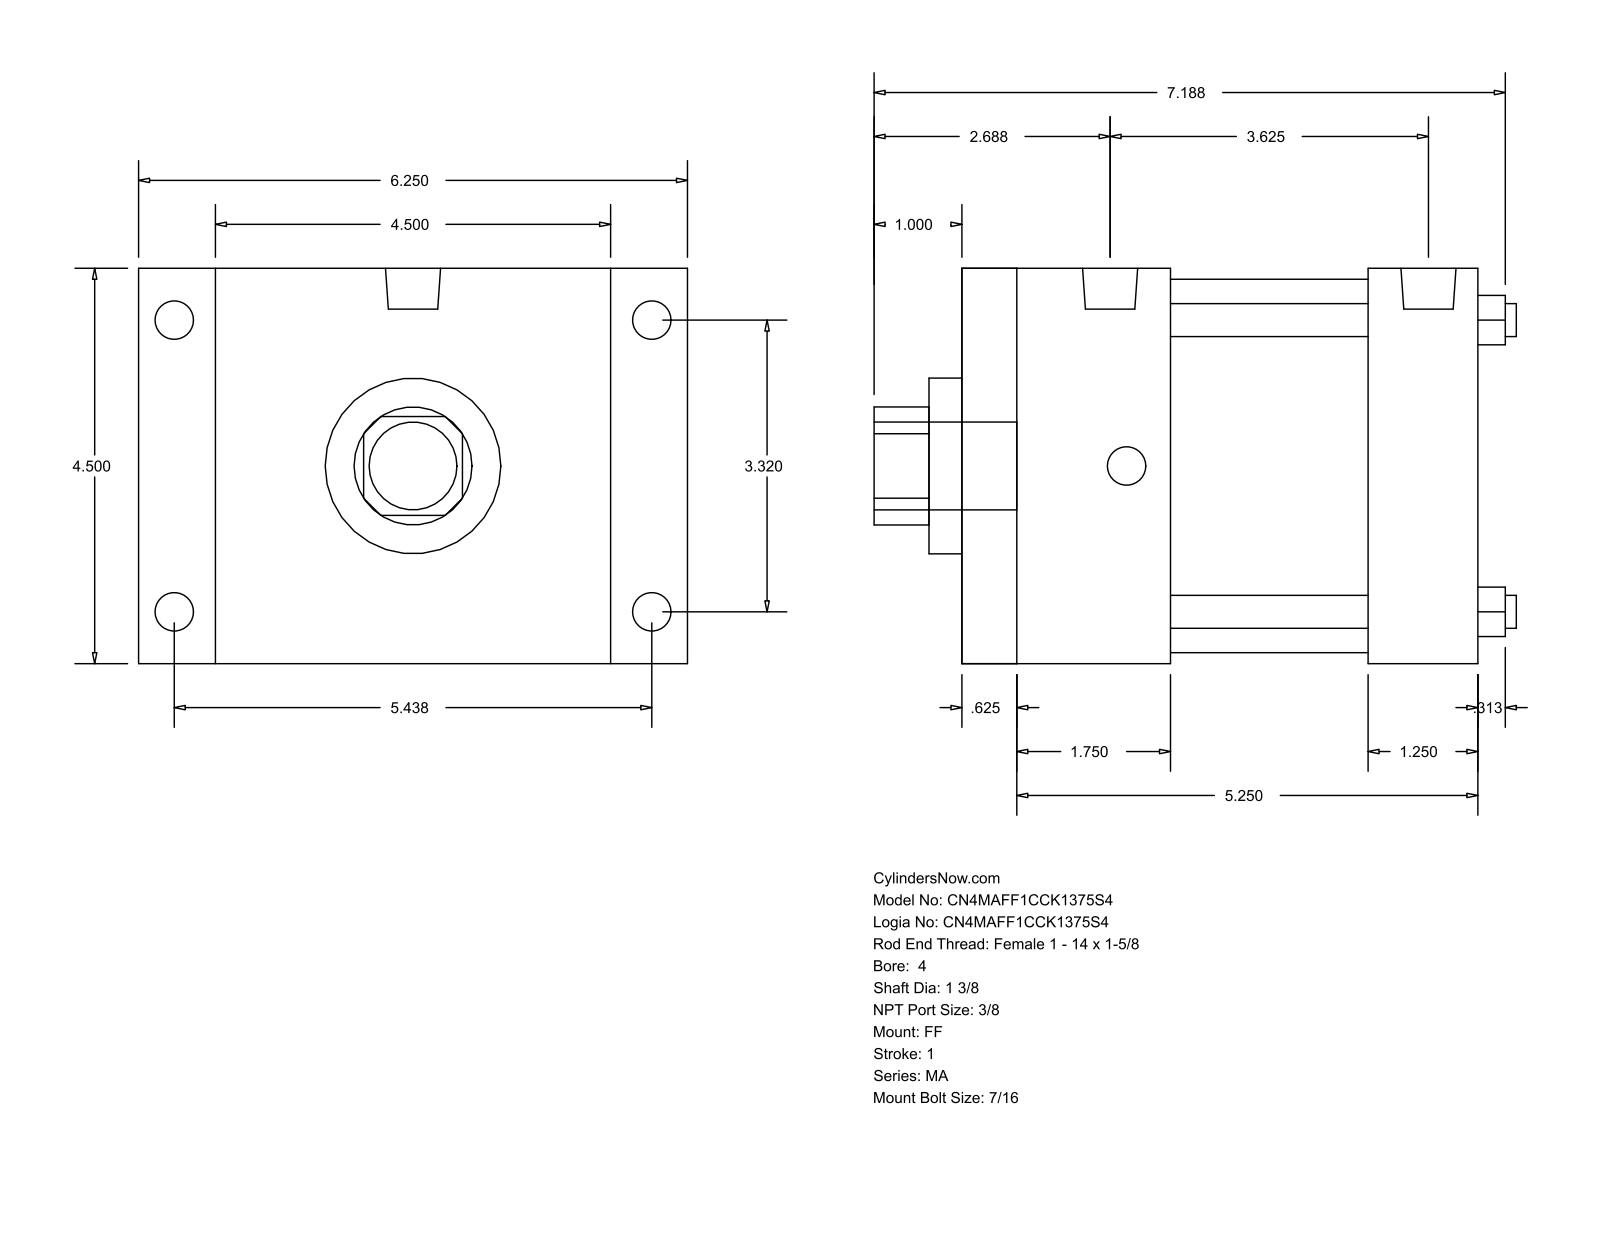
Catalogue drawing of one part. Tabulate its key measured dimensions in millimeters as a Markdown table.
| quantity | value |
| --- | --- |
| part name | MA_FF__0400_1.375 |
| STEP written by | GSSL Pune (CONFIG_CONTROL_DESIGN) |
| units | millimeters |
| bodies | 0 solids, 92 faces (64 planar, 28 cylindrical, 0 other) |
| overall size | 185.74 × 158.75 × 114.3 |
| round holes (diameter × count) | 9.53 × 4, 34.92 × 1, 50.8 × 1, 107.95 × 1 |
| round bosses / shafts (diameter × count) | 11.11 × 8, 15.93 × 2, 25.4 × 1 |
| partial cylindrical surfaces (radius × count) | 17.06 × 1 |
| main face-to-face distances | 114.3, 149.22, 15.87, 133.35, 22.23, 136.53, 117.48, 101.61, 31.74, 60.32 |
| hole center spacings | 59.62, 84.32, 119.25 |
